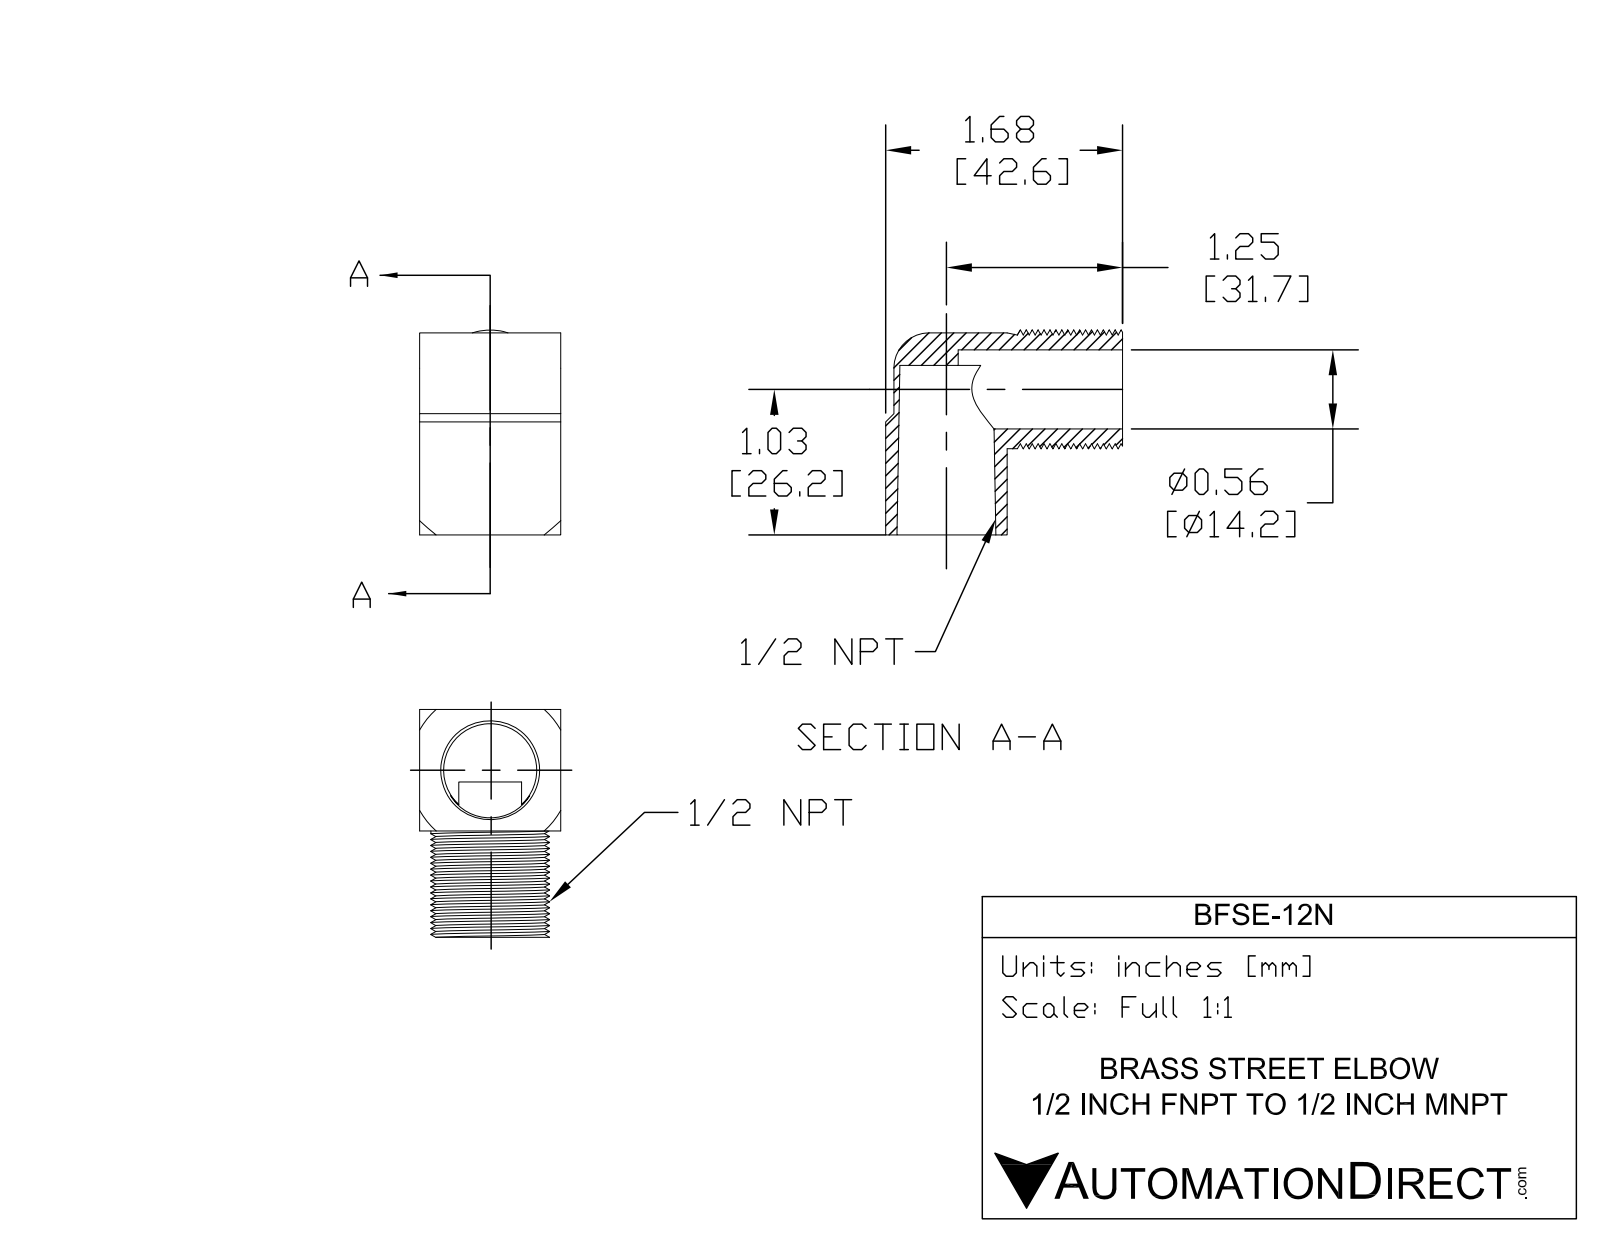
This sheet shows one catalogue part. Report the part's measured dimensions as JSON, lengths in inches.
{"part_name": "BFSE-12N", "step_written_by": "SolidWorks 2015 (CONFIG_CONTROL_DESIGN)", "units": "inches", "bodies": {"solids": 1, "faces": 61, "planar": 12, "cylindrical": 39, "other": 10}, "overall_size": [1.613, 1.45, 1], "volume_in3": 0.904, "surface_area_in2": 14.2, "round_holes": [[0.56, 1]], "round_bosses_or_shafts": [[0.84, 1]], "partial_cylinders_radius": [[0.25, 1]], "face_to_face_distances": [1, 0.86, 1.43, 0.802, 0.058, 0.753, 1.555, 1.613, 1.2, 0.23]}
